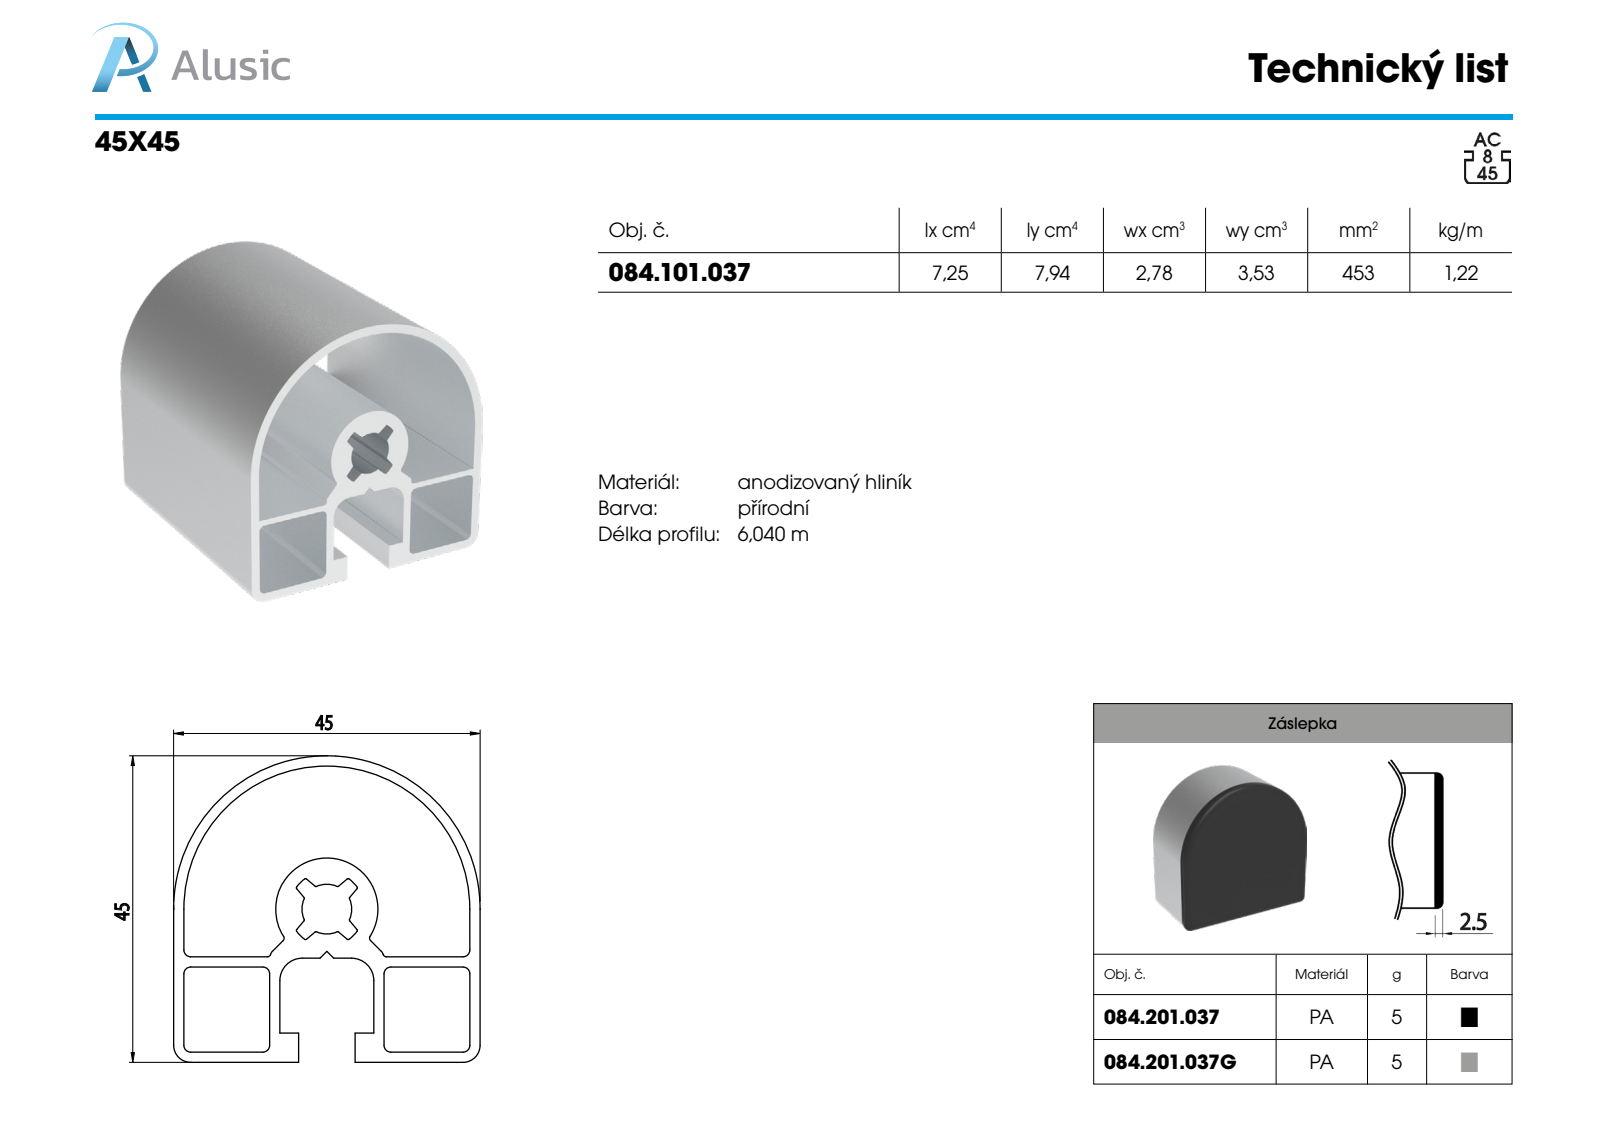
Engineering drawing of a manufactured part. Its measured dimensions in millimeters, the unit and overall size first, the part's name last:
Units: millimetres
Overall size (bounding box): 100 × 45 × 45
Partial cylindrical surfaces — rounded edges, fillets, slot ends (radius × count): R0.2 ×16, R1 ×8, R0.5 ×6, R2.5 ×2, R3 ×2, R3.65 ×1, R5.5 ×1, R7.5 ×1
Main face-to-face distances: 1.5, 43.5, 15, 14, 12.5, 13.5, 1, 14.2, 30.8, 12.7
Volume: 43 639 mm³ · Surface area: 48 759 mm²
Bodies: 1 solid, 93 faces (40 planar, 53 cylindrical, 0 other)
Part name (STEP PRODUCT): 084.101.037
STEP written by: SolidWorks 2018 (AUTOMOTIVE_DESIGN)
